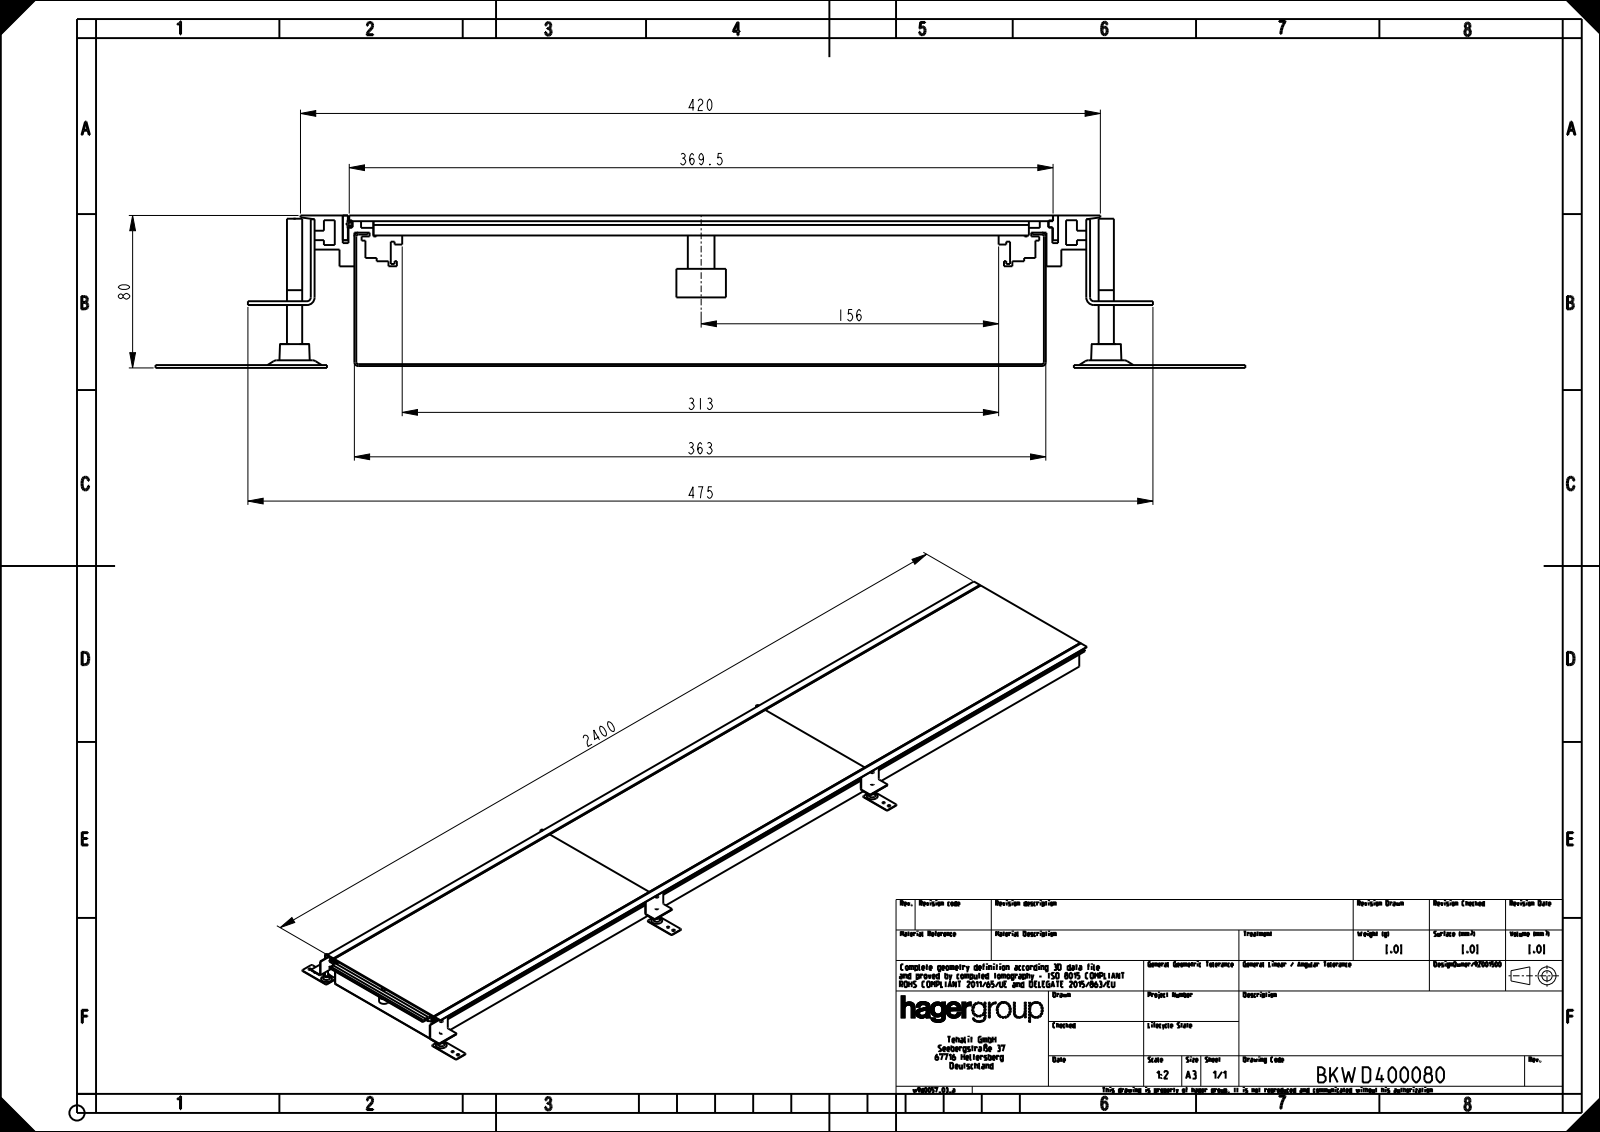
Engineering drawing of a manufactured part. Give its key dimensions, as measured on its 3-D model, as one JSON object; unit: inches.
{"part_name": "U05644KUN; U05650KUN; U05994KUN; U05647KUN (+8 more)", "step_written_by": "CREO PARAMETRIC BY PTC INC, 2020281 (AUTOMOTIVE_DESIGN)", "units": "inches", "bodies": {"solids": 61, "faces": 1036, "planar": 606, "cylindrical": 358, "other": 72}, "overall_size": [95.768, 22.525, 3.15], "volume_in3": 482.9, "surface_area_in2": 10060, "round_holes": [[0.276, 15], [0.315, 9], [0.394, 9], [0.236, 6], [0.335, 6], [0.453, 6], [0.689, 6], [0.906, 6]], "round_bosses_or_shafts": [[1.024, 9], [0.551, 9], [0.469, 9], [0.787, 6], [0.315, 6]], "partial_cylinders_radius": [[0.079, 96], [0.118, 24], [0.02, 20], [0.039, 4], [0.157, 2]], "face_to_face_distances": [0.039, 0.118, 2.992, 3.11, 2.953, 3.071, 14.252, 0.295, 0.256, 0.157], "hole_center_spacings": [31.496, 62.992, 31.506, 31.539, 31.591, 36.492, 36.896, 37.784]}
